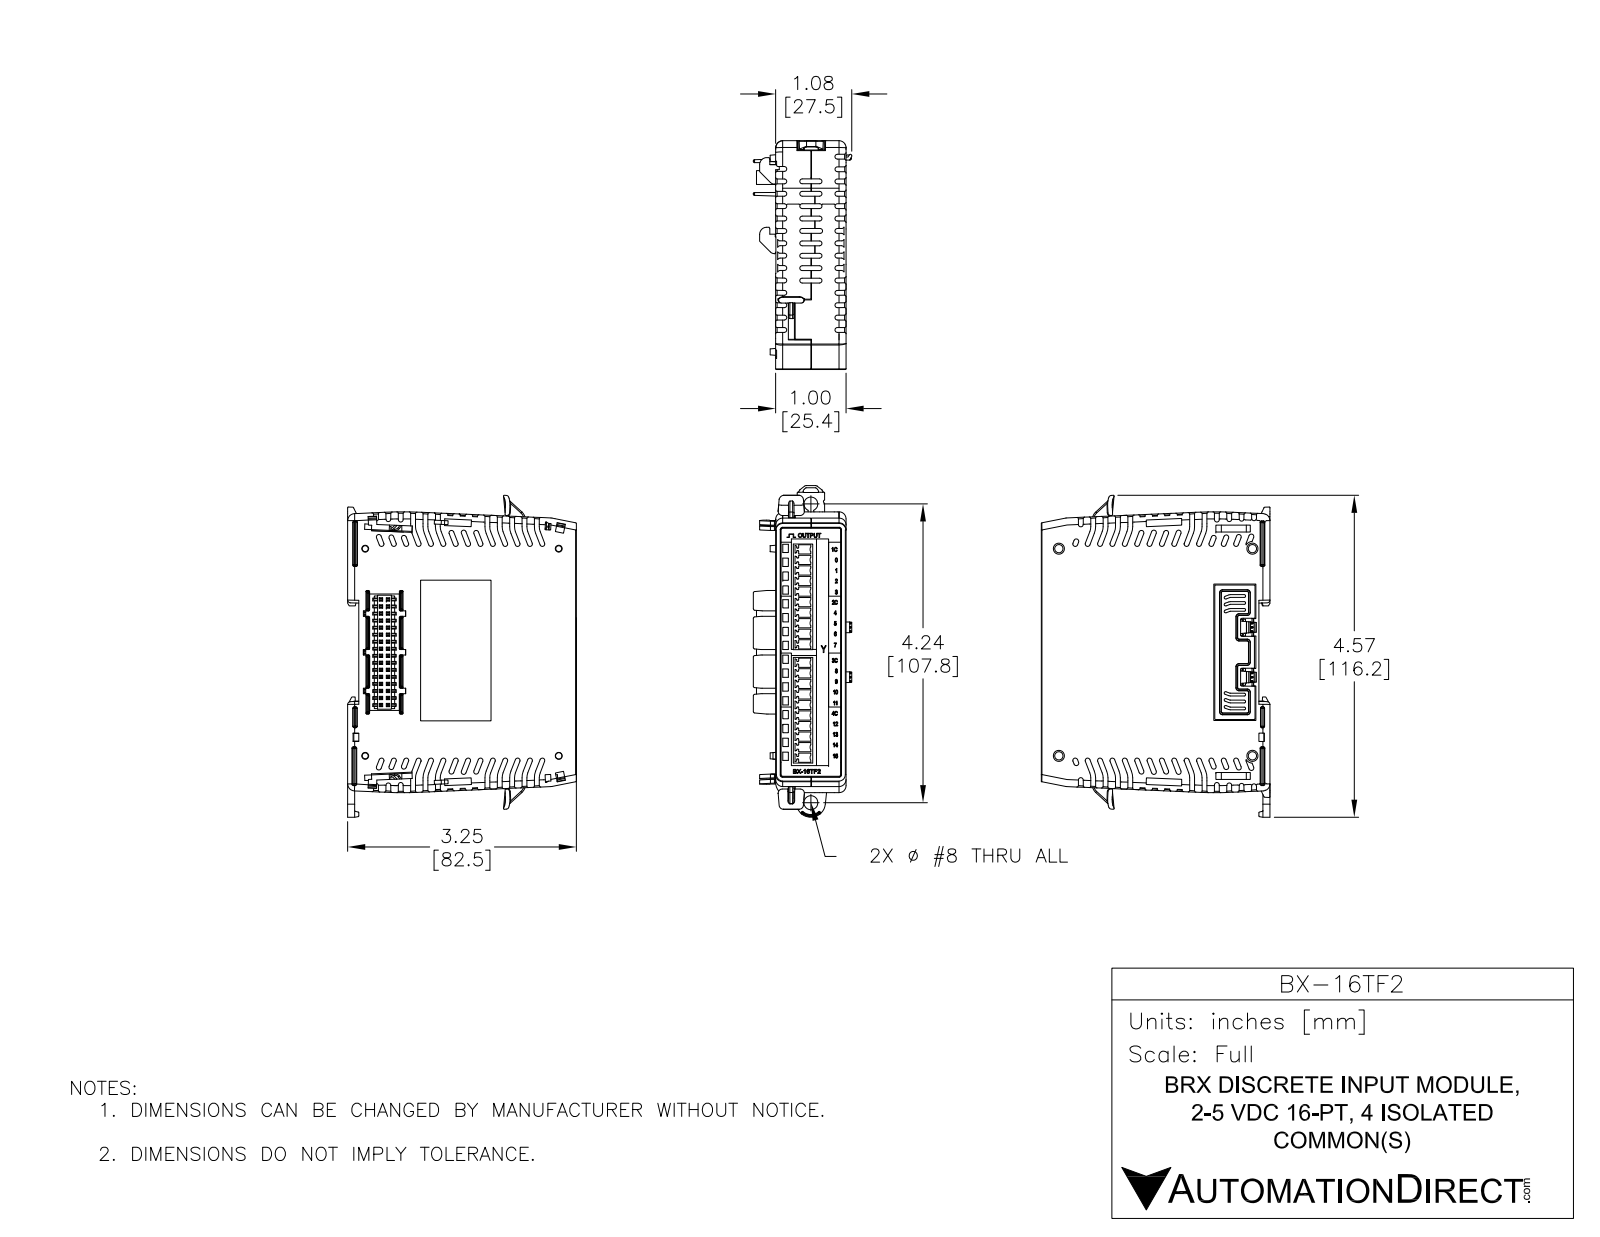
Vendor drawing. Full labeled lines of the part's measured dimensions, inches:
Part name (STEP PRODUCT): BX-16TF2 door and color mod 1 comb 1 fXT c2
STEP written by: SolidWorks 2017 (AUTOMOTIVE_DESIGN)
Units: inches
Bodies: 14 solids, 3871 faces (2881 planar, 477 cylindrical, 513 other)
Overall size (bounding box): 4.586 × 3.25 × 1.4
Volume: 11.58 in³ · Surface area: 72.2 in²
Round holes (diameter × count): ⌀0.047 ×2, ⌀0.065 ×2, ⌀0.118 ×2, ⌀0.118 ×2, ⌀0.199 ×1
Round bosses / shafts (diameter × count): ⌀0.062 ×2, ⌀0.059 ×2
Partial cylindrical surfaces — rounded edges, fillets, slot ends (radius × count): R0.008 ×101, R0.01 ×46, R0.005 ×24, R0.02 ×22, R0.062 ×20, R0.117 ×14, R0.039 ×13, R0.01 ×12
Main face-to-face distances: 1, 3.211, 3.22, 0.039, 0.475, 0.157, 3.053, 3.063, 0.1, 0.052
Hole centre spacings: 0.1, 0.824, 0.919, 1.3, 2.093, 2.193, 2.585, 2.617
